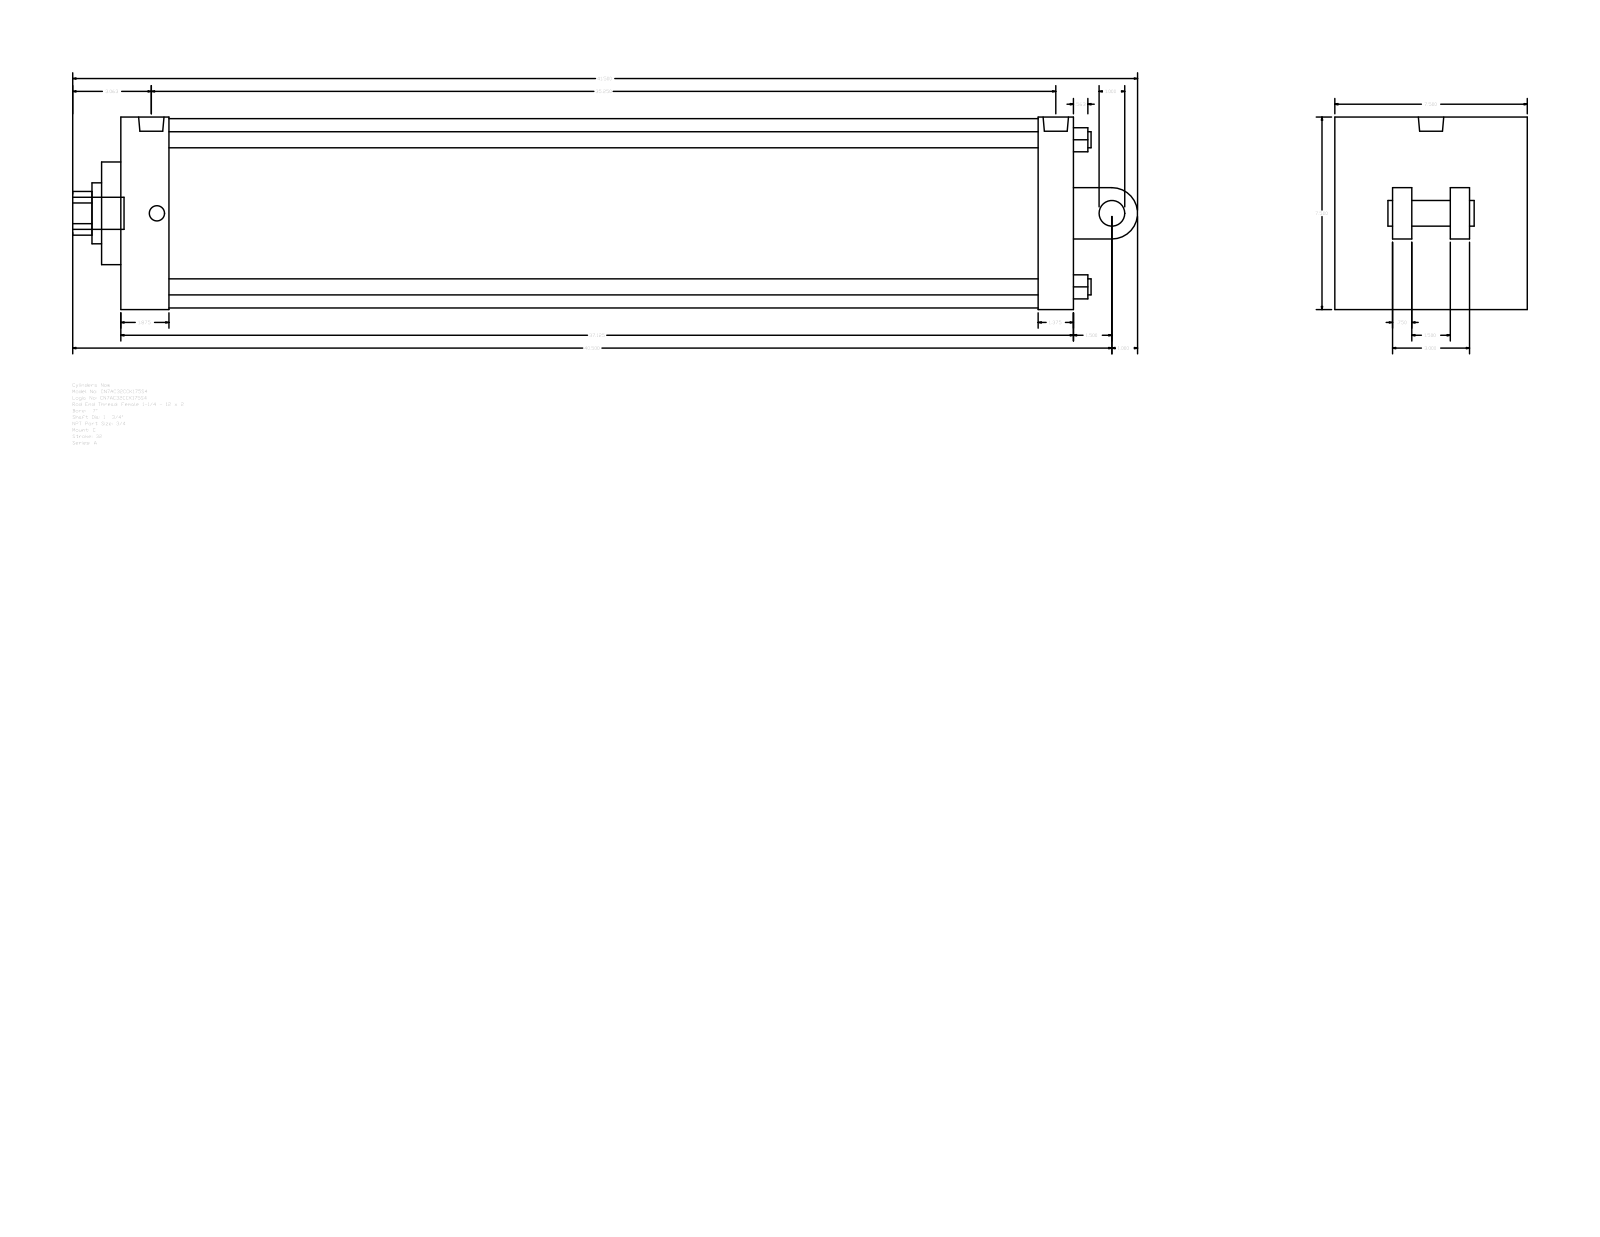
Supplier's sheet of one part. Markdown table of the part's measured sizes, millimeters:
| quantity | value |
| --- | --- |
| part name | A_C__0700_1.75 |
| STEP written by | GSSL Pune (CONFIG_CONTROL_DESIGN) |
| units | millimeters |
| bodies | 0 solids, 104 faces (75 planar, 29 cylindrical, 0 other) |
| overall size | 1054.1 × 190.5 × 190.5 |
| round holes (diameter × count) | 15.88 × 4, 15.08 × 2, 25.12 × 1, 44.45 × 1, 60.33 × 1, 187.32 × 1 |
| round bosses / shafts (diameter × count) | 15.08 × 2, 31.75 × 1, 25.4 × 1, 25.12 × 1 |
| partial cylindrical surfaces (radius × count) | 21.63 × 1, 25.4 × 1 |
| main face-to-face distances | 190.5, 942.98, 19.05, 76.2, 57.15, 44.45, 47.63, 895.35, 908.05, 860.42 |
| hole center spacings | 102.91, 145.54, 205.82, 5.56 |
